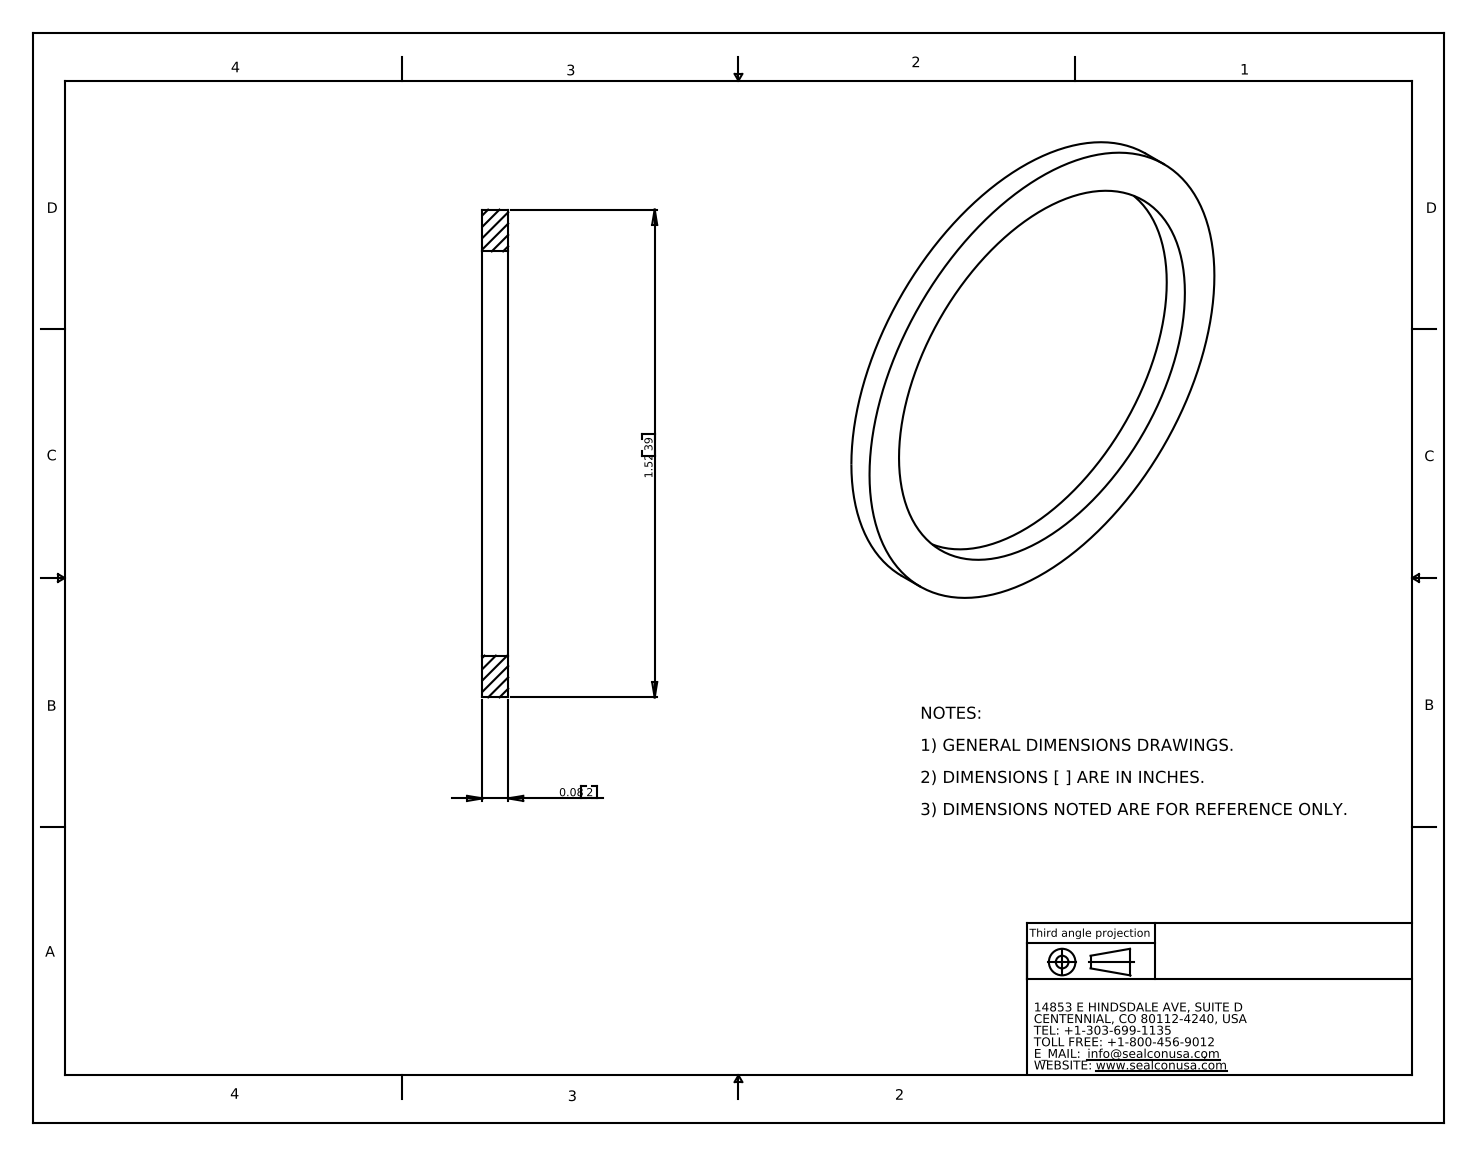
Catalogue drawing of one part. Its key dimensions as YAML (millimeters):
part_name: "SM-32-VT"
step_written_by: "SolidWorks 2007 (CONFIG_CONTROL_DESIGN)"
units: millimeters
bodies: {solids: 1, faces: 6, planar: 2, cylindrical: 4, other: 0}
overall_size: [38.6, 38.6, 2]
volume: 740
surface_area: 1183
round_holes:
  - {diameter: 32, count: 1}
round_bosses_or_shafts:
  - {diameter: 38.6, count: 1}
face_to_face_distances: [2]
